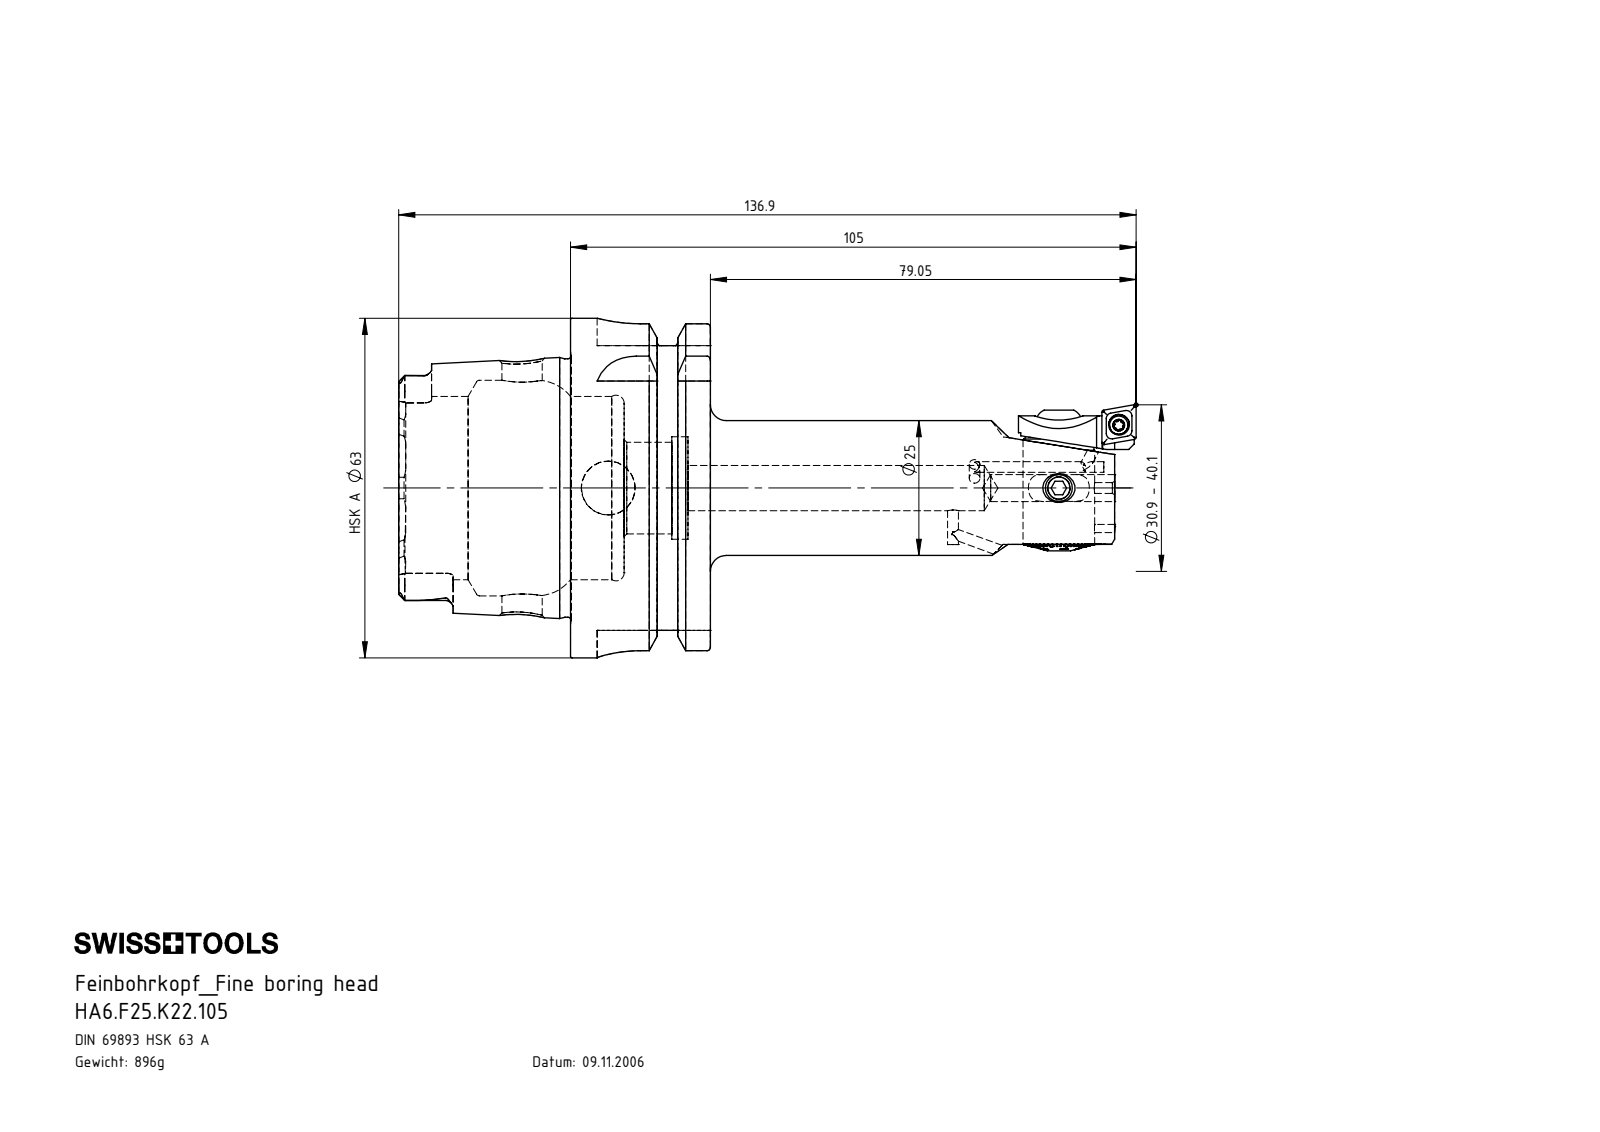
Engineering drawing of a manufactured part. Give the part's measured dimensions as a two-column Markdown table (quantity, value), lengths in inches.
| quantity | value |
| --- | --- |
| part name | CCMT060204; F25-BG2.013.004_A; F25-BG1.009.006_A; F25-ER1.101.008_A (+8 more) |
| STEP written by | SolidWorks 2022 (CONFIG_CONTROL_DESIGN) |
| units | inches |
| bodies | 16 solids, 920 faces (378 planar, 187 cylindrical, 355 other) |
| overall size | 5.39 × 2.48 × 2.48 |
| volume | 7.001 in³ |
| surface area | 54.98 in² |
| round holes (diameter × count) | 0.079 × 4, 0.081 × 3, 0.165 × 2, 0.295 × 2, 0.394 × 2, 0.083 × 1, 0.094 × 1, 0.106 × 1, 0.11 × 1, 0.118 × 1, 0.152 × 1, 0.197 × 1 |
| round bosses / shafts (diameter × count) | 0.197 × 2, 0.195 × 2, 0.098 × 2, 2.48 × 1, 2.163 × 1, 1.887 × 1, 0.984 × 1, 0.511 × 1 |
| partial cylindrical surfaces (radius × count) | 0.008 × 6, 0.055 × 6, 0.014 × 4, 0.02 × 4, 0.113 × 4, 0.315 × 4, 0.014 × 2, 0.052 × 2 |
| main face-to-face distances | 1.022, 0.63, 0.392, 1.256, 1.648, 2.278, 2.079, 0.858, 0.467, 5.278 |
| hole center spacings | 0.151, 0.157, 0.176, 0.268, 0.372, 0.728, 3.195, 3.293 |
